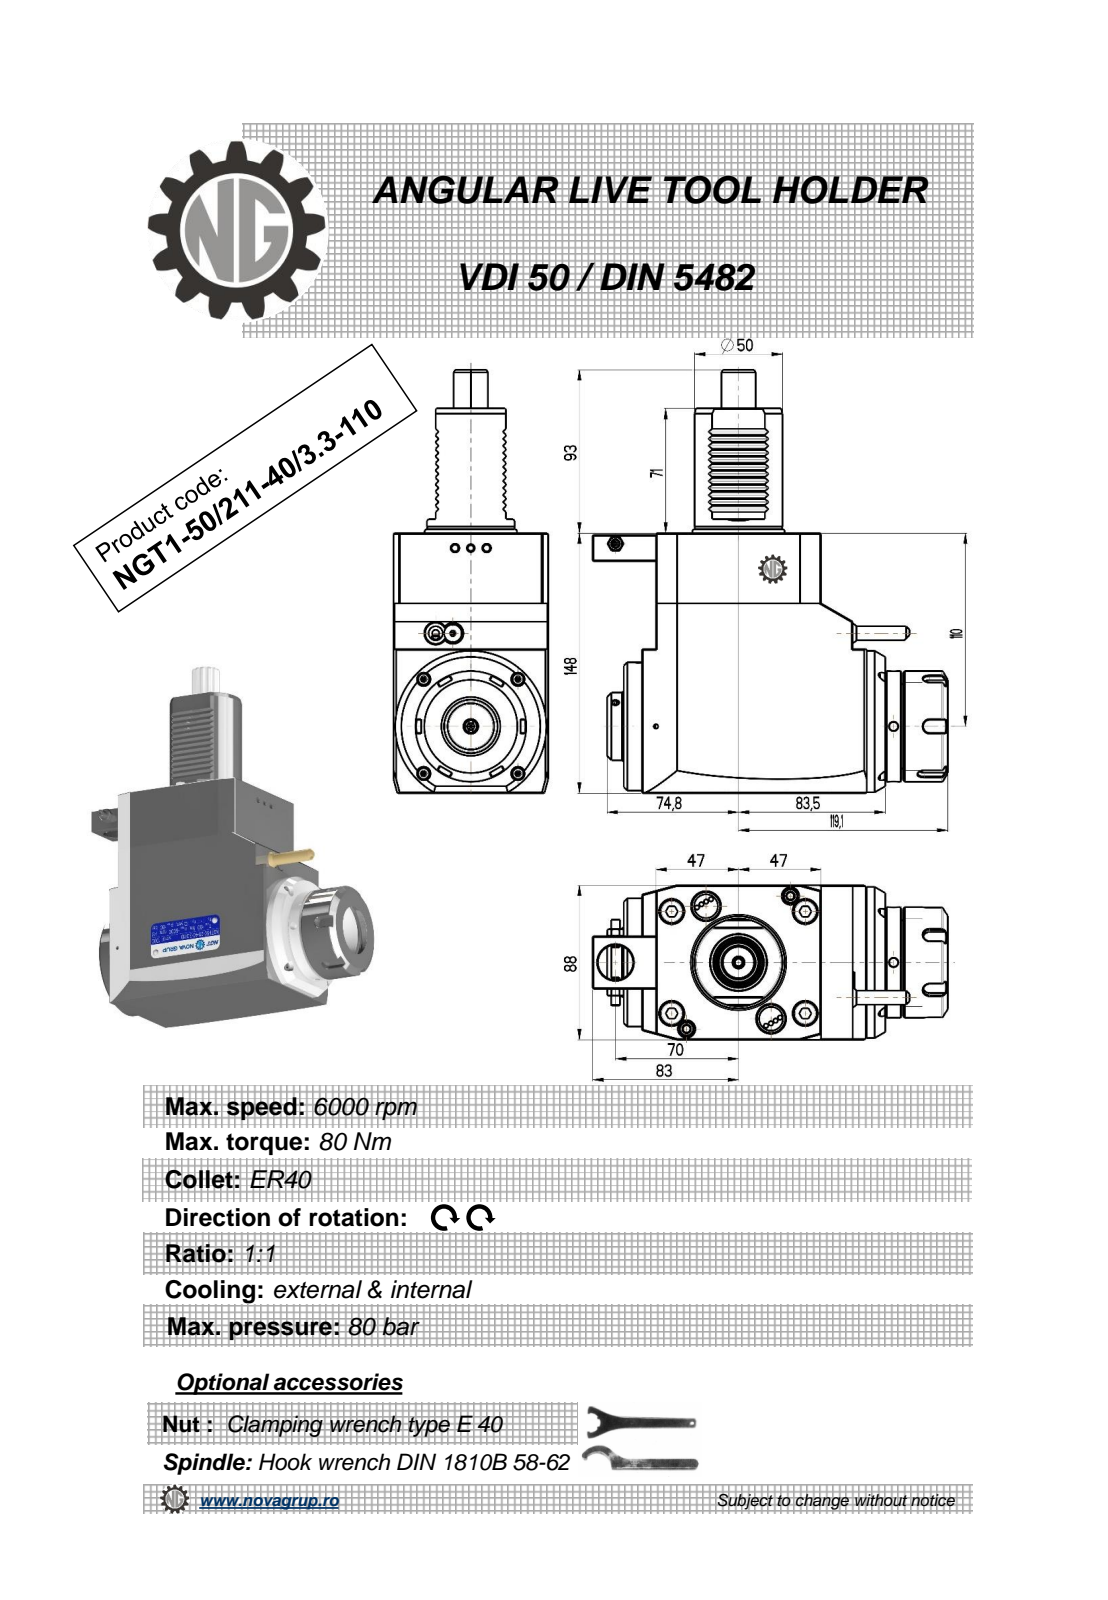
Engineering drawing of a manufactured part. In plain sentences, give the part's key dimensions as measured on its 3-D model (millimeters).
The part is named "NGT1_50_211_40_3_3_110". Its 3-D file was written by "PRO/ENGINEER BY PARAMETRIC TECHNOLOGY CORPORATION, 2010280 (CONFIG_CONTROL_DESIGN)". It is 1 solid with 544 faces: 243 planar, 154 cylindrical and 147 other. Overall it measures 241 by 202.1 by 88 millimeters. Its volume is 1 837 000 cubic millimeters and its surface area 116 622 square millimeters. Round holes: 3 of diameter 5, 1 of diameter 3, 1 of diameter 4.2, 1 of diameter 5.3, 1 of diameter 9.5, 1 of diameter 20, 1 of diameter 33.5. Round bosses or shafts: 1 of diameter 86, 1 of diameter 73, 1 of diameter 63, 1 of diameter 51, 1 of diameter 50, 1 of diameter 38.5, 1 of diameter 10, 1 of diameter 8.96. Partial cylindrical surfaces (rounded edges, fillets, slot ends): 24 of radius 0.3, 24 of radius 3.33, 12 of radius 0.26, 6 of radius 0.2, 5 of radius 3.75, 1 of radius 8.25, 1 of radius 9.75. The main face-to-face distances are 88, 148, 8, 94, 130.5, 36.5, 120, 18.3, 112.3, 148.8. The hole center spacings are 52.46, 56.65, 70, 88.25, 101.5, 158.25.
